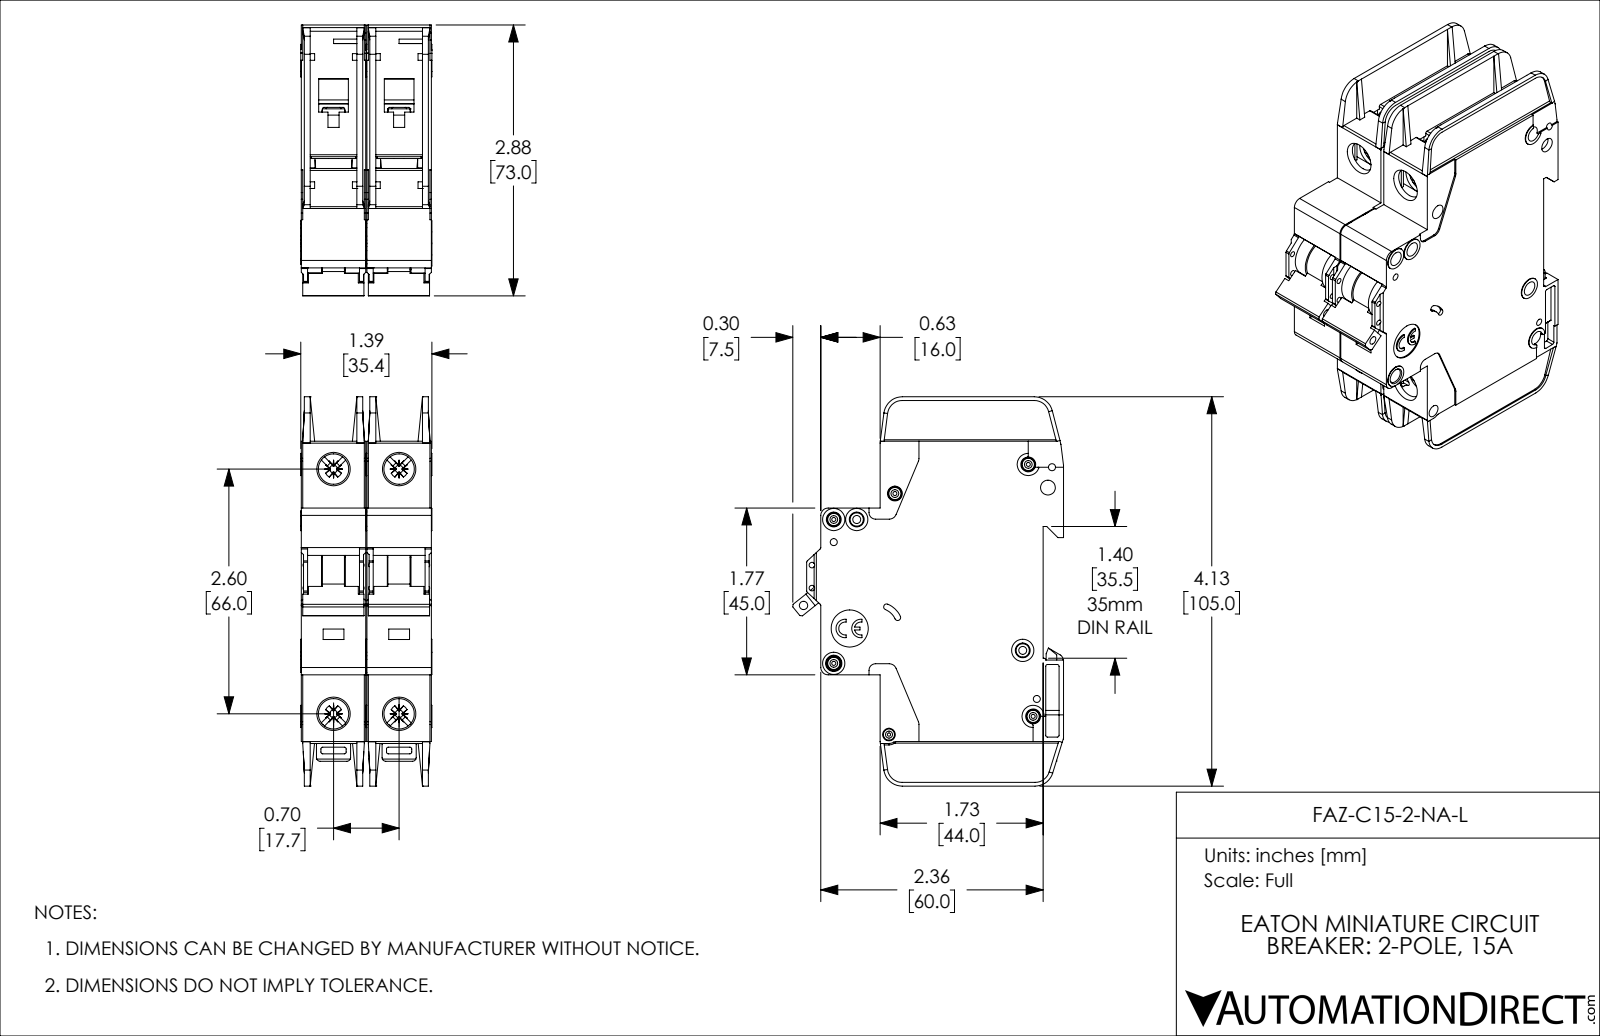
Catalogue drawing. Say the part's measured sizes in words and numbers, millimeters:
The part is named "FAZ-C15-2-NA-L". Its 3-D file was written by "SolidWorks 2019 (AUTOMOTIVE_DESIGN)". It is 2 solids with 2254 faces: 1342 planar, 714 cylindrical and 198 other. Overall it measures 105 by 73.1 by 35.4 millimeters. Its volume is 153 500 cubic millimeters and its surface area 52 910 square millimeters. Round holes: 8 of diameter 4, 5 of diameter 1.1, 4 of diameter 1.9, 4 of diameter 8.2, 2 of diameter 1.5, 2 of diameter 2.2, 1 of diameter 0.9, 1 of diameter 2.3, 1 of diameter 2.5, 1 of diameter 3.4, 1 of diameter 10. Round bosses or shafts: 5 of diameter 3.3, 4 of diameter 6, 3 of diameter 3, 2 of diameter 2.5. Partial cylindrical surfaces (rounded edges, fillets, slot ends): 57 of radius 0.5, 20 of radius 0.4, 14 of radius 1, 10 of radius 2, 8 of radius 1.1, 5 of radius 0.2, 5 of radius 5, 4 of radius 0.3. The main face-to-face distances are 17.7, 1.2, 17.4, 15, 2.4, 16.2, 13.8, 35.1, 18.9, 16.5. The hole center spacings are 6.2, 13.6, 17.7, 22.1, 66, 68.3, 4.8, 5.1.
